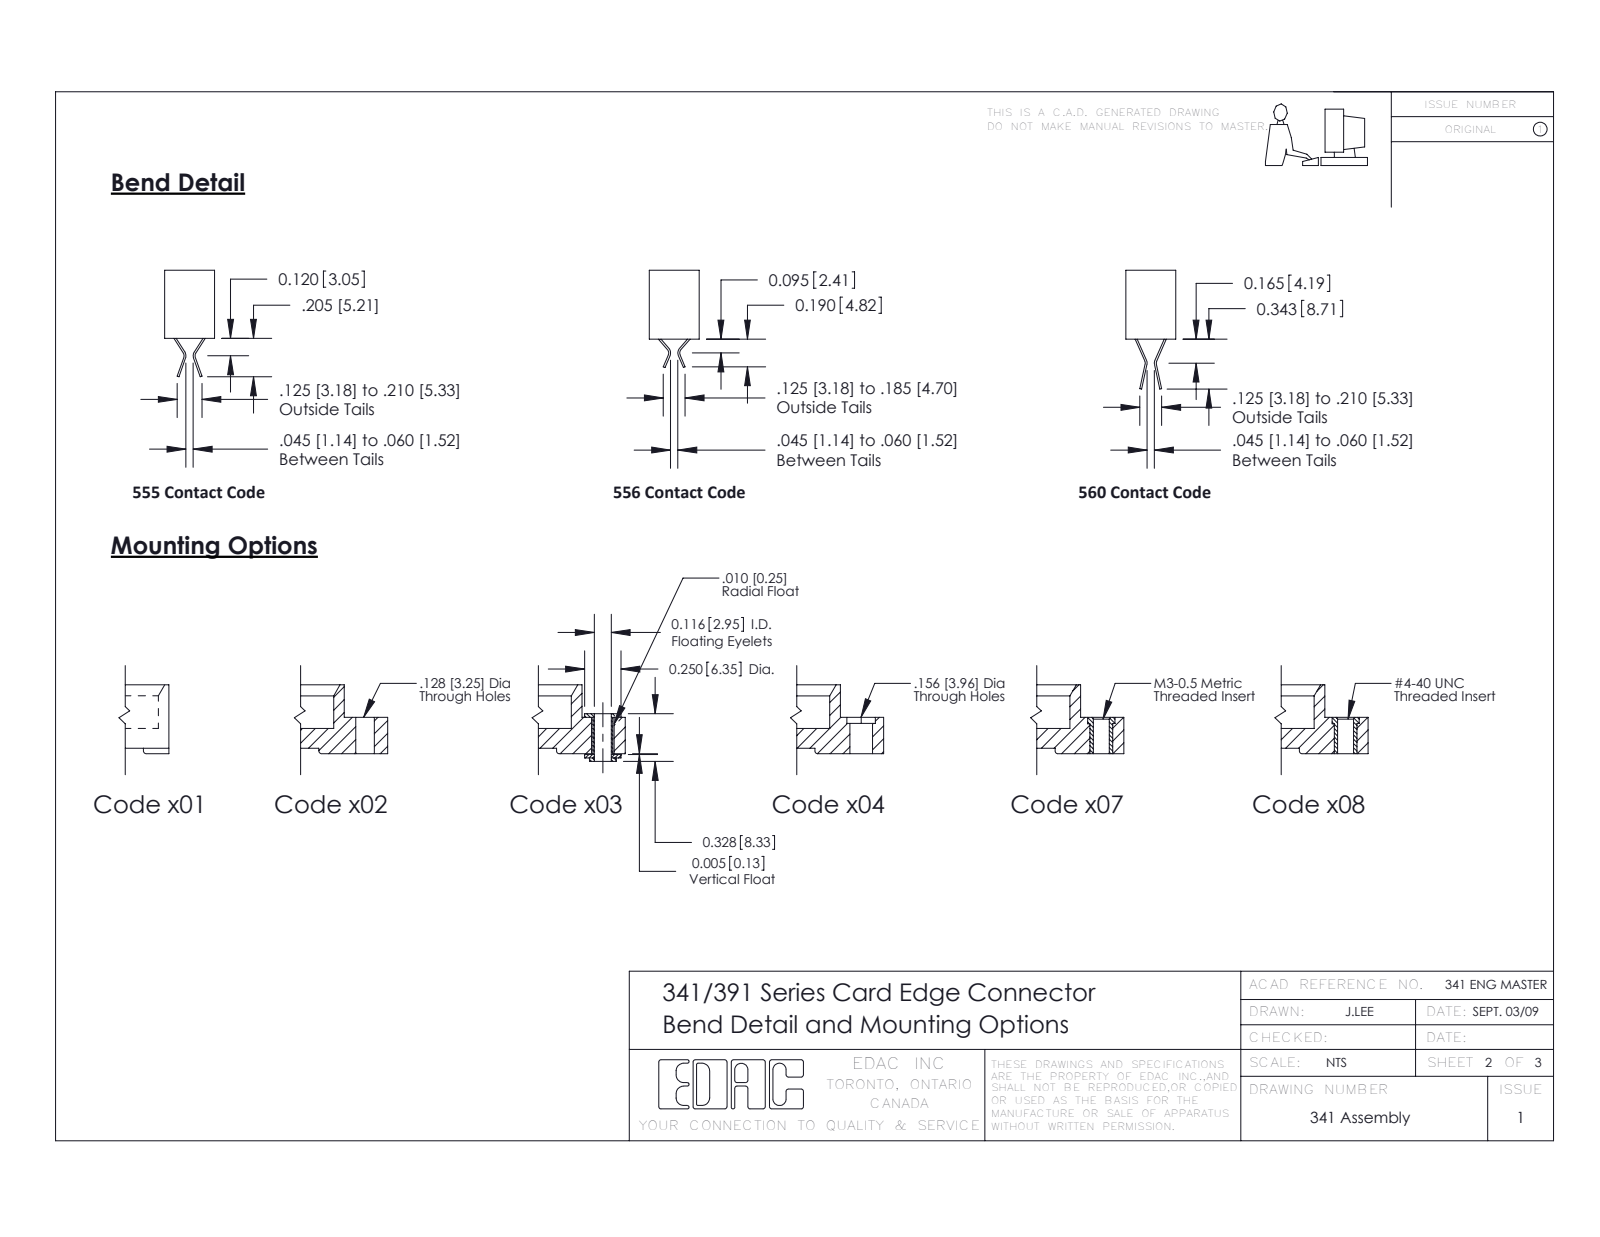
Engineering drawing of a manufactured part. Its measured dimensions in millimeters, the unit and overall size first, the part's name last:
Units: millimetres
Overall size (bounding box): 52.7 × 16.7 × 8.4
Round holes (diameter × count): ⌀3.3 ×2
Partial cylindrical surfaces — rounded edges, fillets, slot ends (radius × count): R0.4 ×74, R0.5 ×25, R0.1 ×24, R0.3 ×24, R0.3 ×22, R0.6 ×12, R0.2 ×6, R0.8 ×6
Main face-to-face distances: 2.5, 5.1, 7.6, 8.4, 10.2, 0.3, 1, 7.3, 12.7, 15.2
Hole centre spacings: 45.1
Volume: 2 920 mm³ · Surface area: 4 746 mm²
Bodies: 13 solids, 1100 faces (656 planar, 396 cylindrical, 48 other)
Part name (STEP PRODUCT): 341-292-001_341-292-100; 341-012-500-102; 341 Part_.128 (3.25) Dia Mounting Holes
STEP written by: SolidWorks 2016 (CONFIG_CONTROL_DESIGN)
